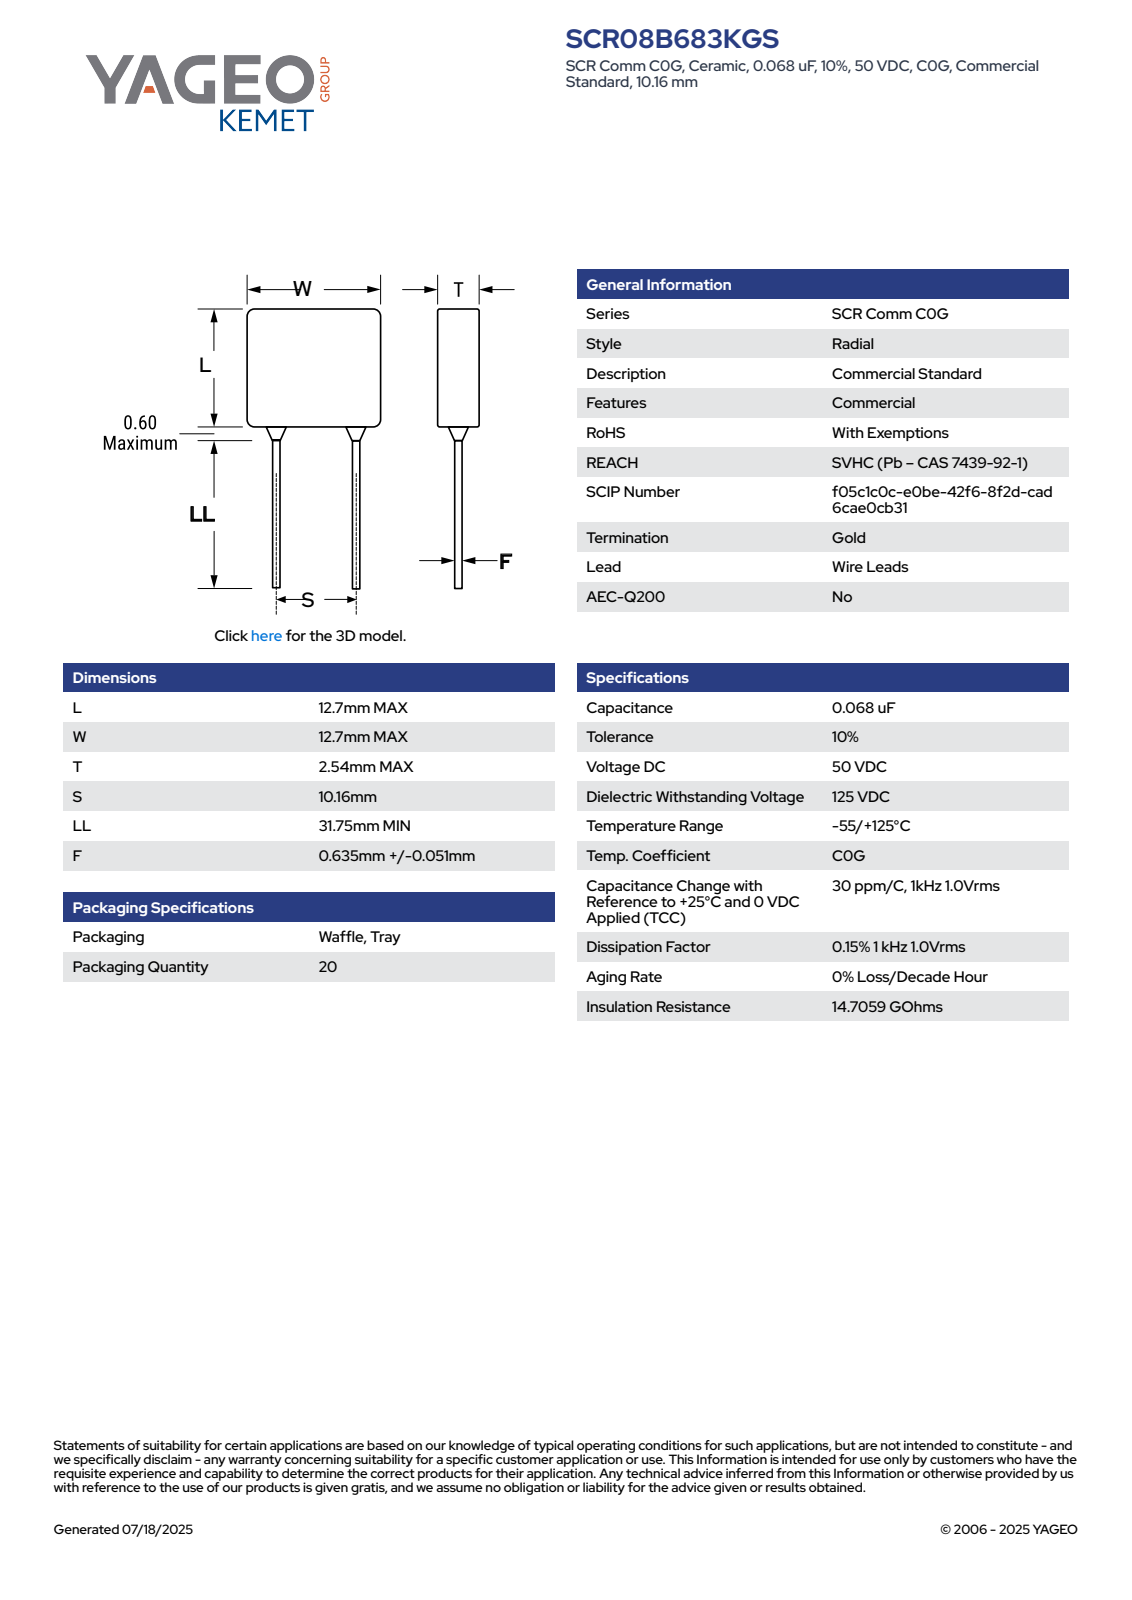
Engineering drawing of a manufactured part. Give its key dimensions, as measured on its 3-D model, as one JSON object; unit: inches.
{"part_name": "CCR_C3_8_L12.7T2.54S10.922LL31.75F0.686W12.7", "step_written_by": "SolidWorks 2021 (AUTOMOTIVE_DESIGN)", "units": "inches", "bodies": {"solids": 4, "faces": 77, "planar": 65, "cylindrical": 8, "other": 4}, "overall_size": [1.774, 0.5, 0.1], "volume_in3": 0.026, "surface_area_in2": 0.953, "round_bosses_or_shafts": [[0.027, 2]], "partial_cylinders_radius": [[0.02, 4]], "face_to_face_distances": [0.1, 0.5, 0.098, 1.274, 1.774, 1.562, 0.288, 0.212, 1.482, 0.209]}
